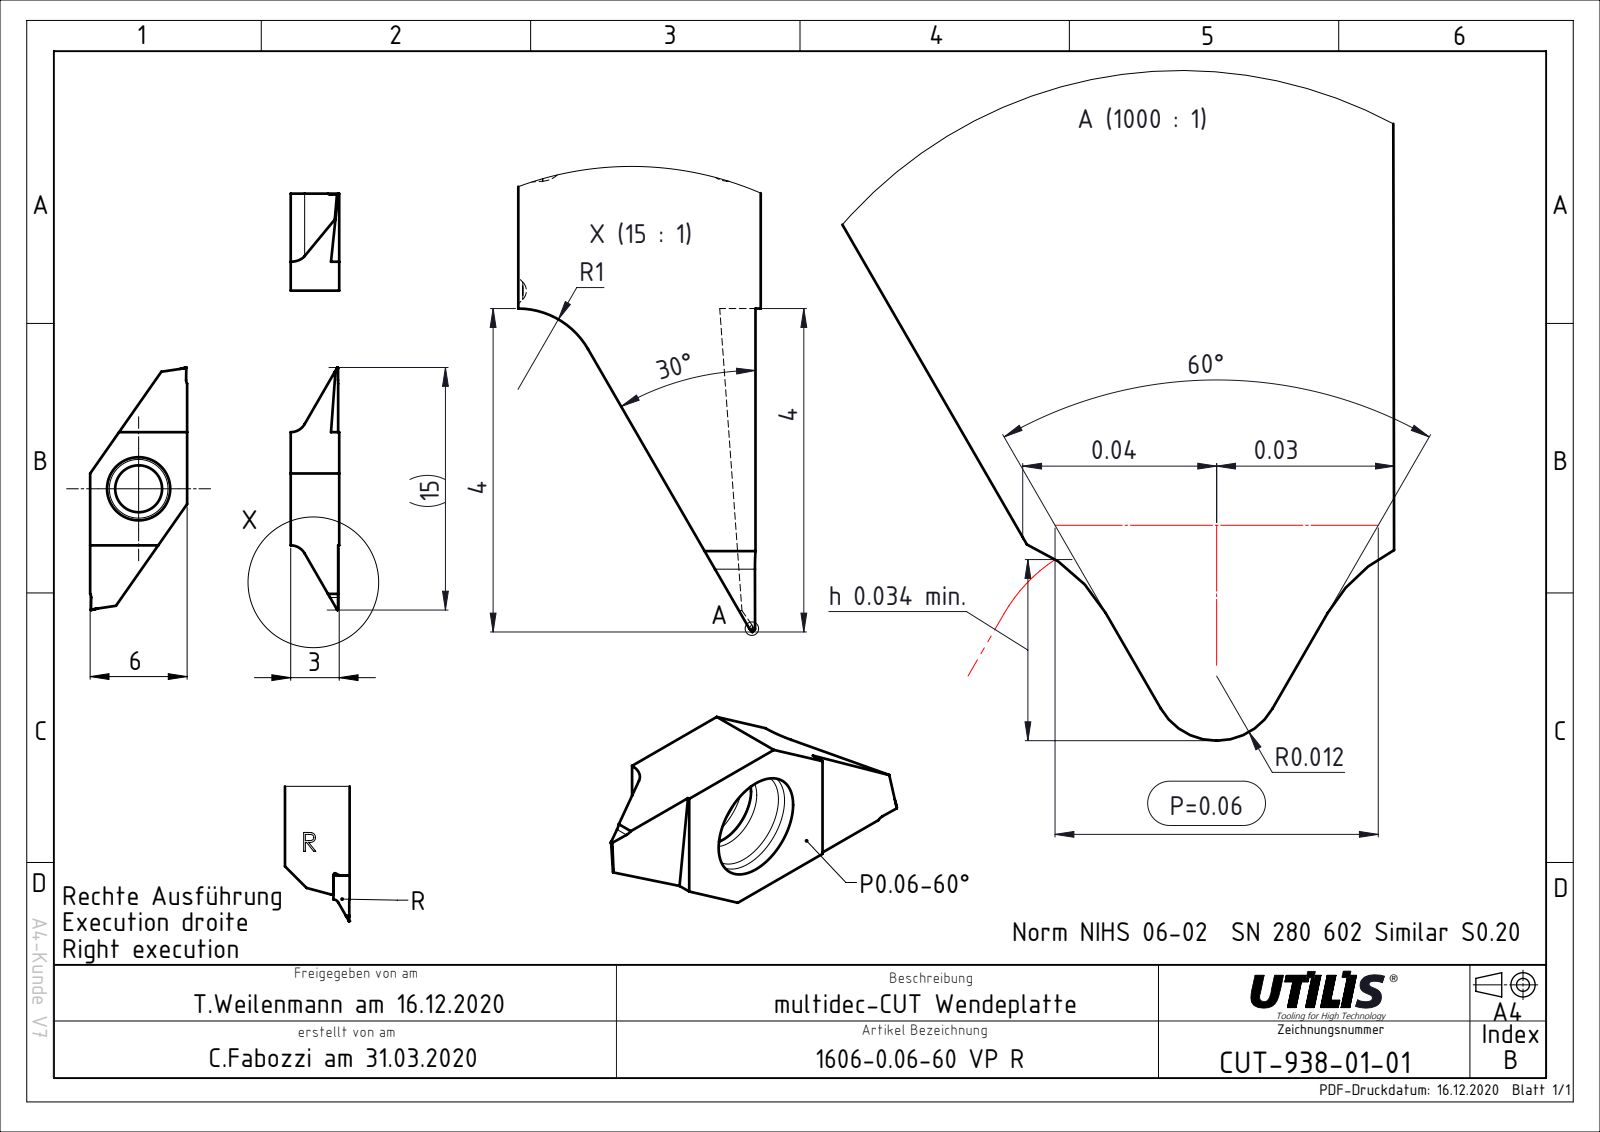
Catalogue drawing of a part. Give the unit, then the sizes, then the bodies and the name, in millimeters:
Units: millimetres
Overall size (bounding box): 15 × 6 × 3
Round holes (diameter × count): ⌀2.9 ×1
Partial cylindrical surfaces — rounded edges, fillets, slot ends (radius × count): R1 ×2
Main face-to-face distances: 6, 3, 9, 7, 12, 7.18, 7.19
Volume: 123 mm³ · Surface area: 208 mm²
Bodies: 1 solid, 36 faces (22 planar, 14 cylindrical, 0 other)
Part name (STEP PRODUCT): CUT-938-01; ASME Y14.5
STEP written by: FormatWorks Professional (AP242_MANAGED_MODEL_BASED_3D_ENGINEERING_MIM_LF)
